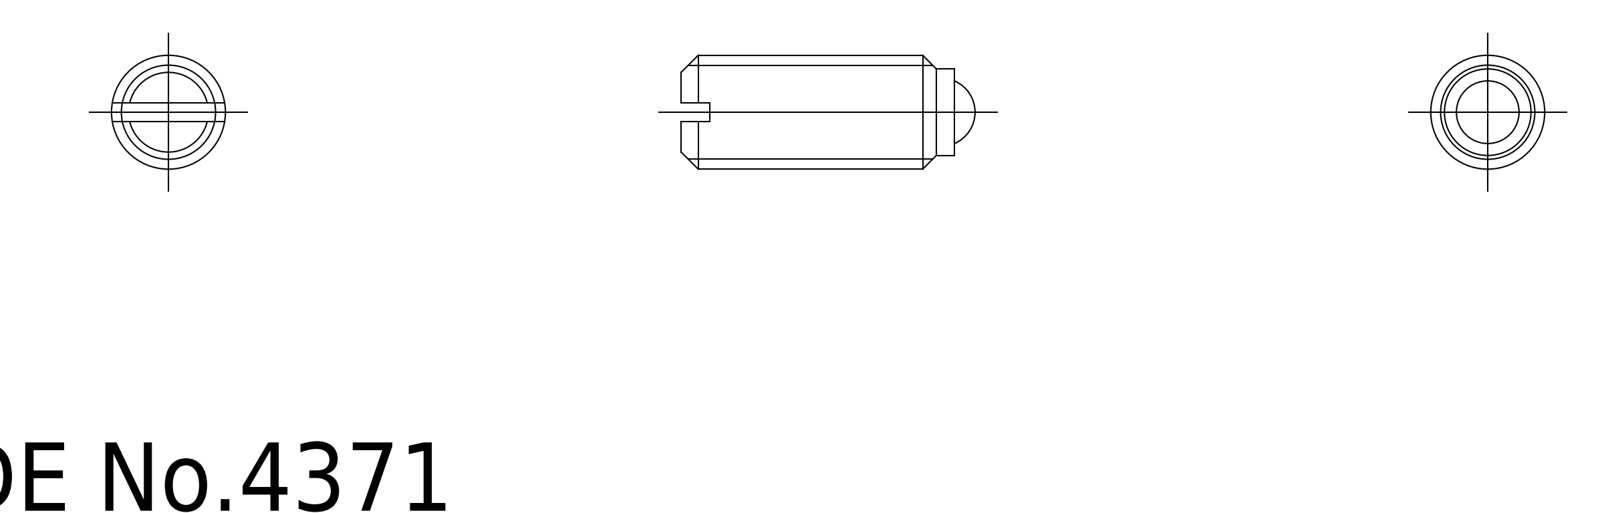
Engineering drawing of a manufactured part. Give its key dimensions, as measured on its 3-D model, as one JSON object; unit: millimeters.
{"part_name": "ball; PBF_5_KN_14622_36", "step_written_by": "CADfix (AUTOMOTIVE_DESIGN)", "units": "millimeters", "bodies": {"solids": 2, "faces": 19, "planar": 0, "cylindrical": 0, "other": 19}, "overall_size": [12.9, 5, 5], "volume_mm3": 207, "surface_area_mm2": 283}
